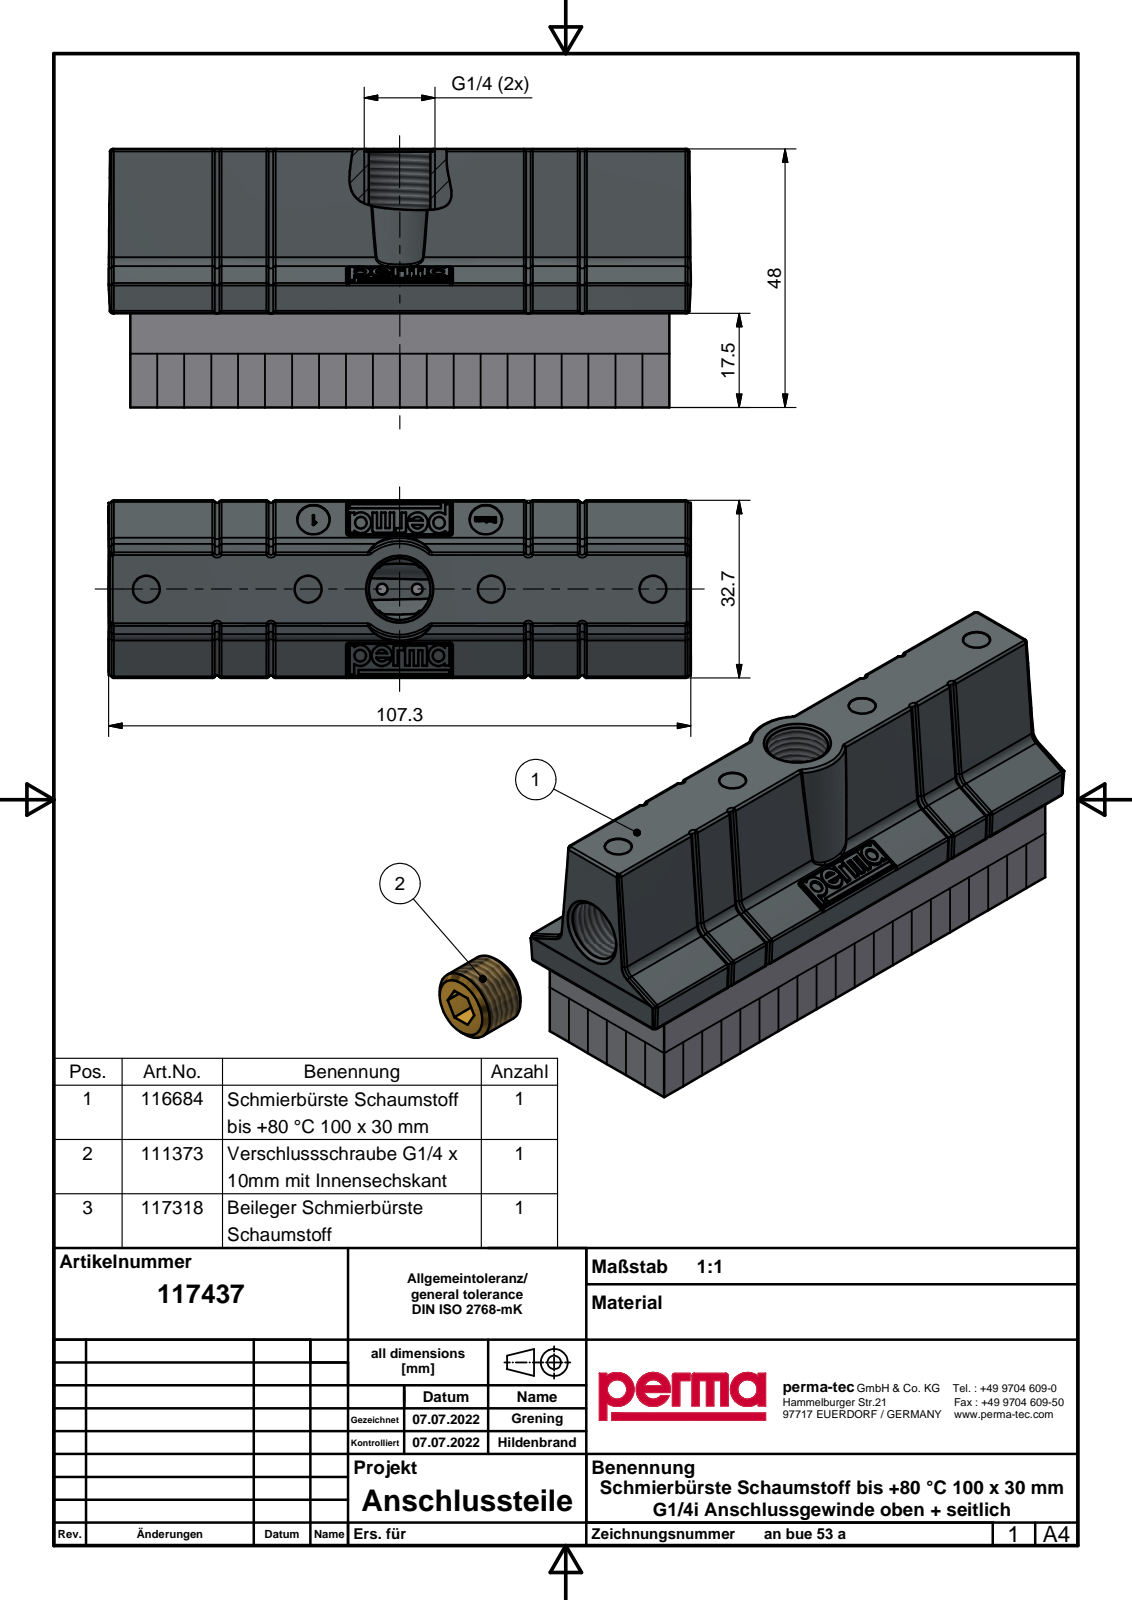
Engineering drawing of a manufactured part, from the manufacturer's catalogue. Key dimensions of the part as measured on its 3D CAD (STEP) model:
Part name (STEP PRODUCT): anbue53; anbue50; anbue50_p01; anbue50_p02 (+1 more)
STEP written by: Autodesk Inventor 2022 (CONFIG_CONTROL_DESIGN)
Units: millimetres
Bodies: 3 solids, 849 faces (395 planar, 159 cylindrical, 295 other)
Overall size (bounding box): 108 × 48 × 32.99
Volume: 111 228 mm³ · Surface area: 30 025 mm²
Round holes (diameter × count): ⌀2 ×12, ⌀5 ×4, ⌀6 ×2, ⌀11.45 ×2
Round bosses / shafts (diameter × count): ⌀13.16 ×1
Partial cylindrical surfaces — rounded edges, fillets, slot ends (radius × count): R0.5 ×86, R2 ×6, R1 ×5, R4.25 ×1
Main face-to-face distances: 20, 20.05, 30, 48, 28, 27.95, 100, 17.5, 2.5, 2.55
Hole centre spacings: 7, 14, 47.5, 13.75, 21, 40.5, 54.5, 6.5
